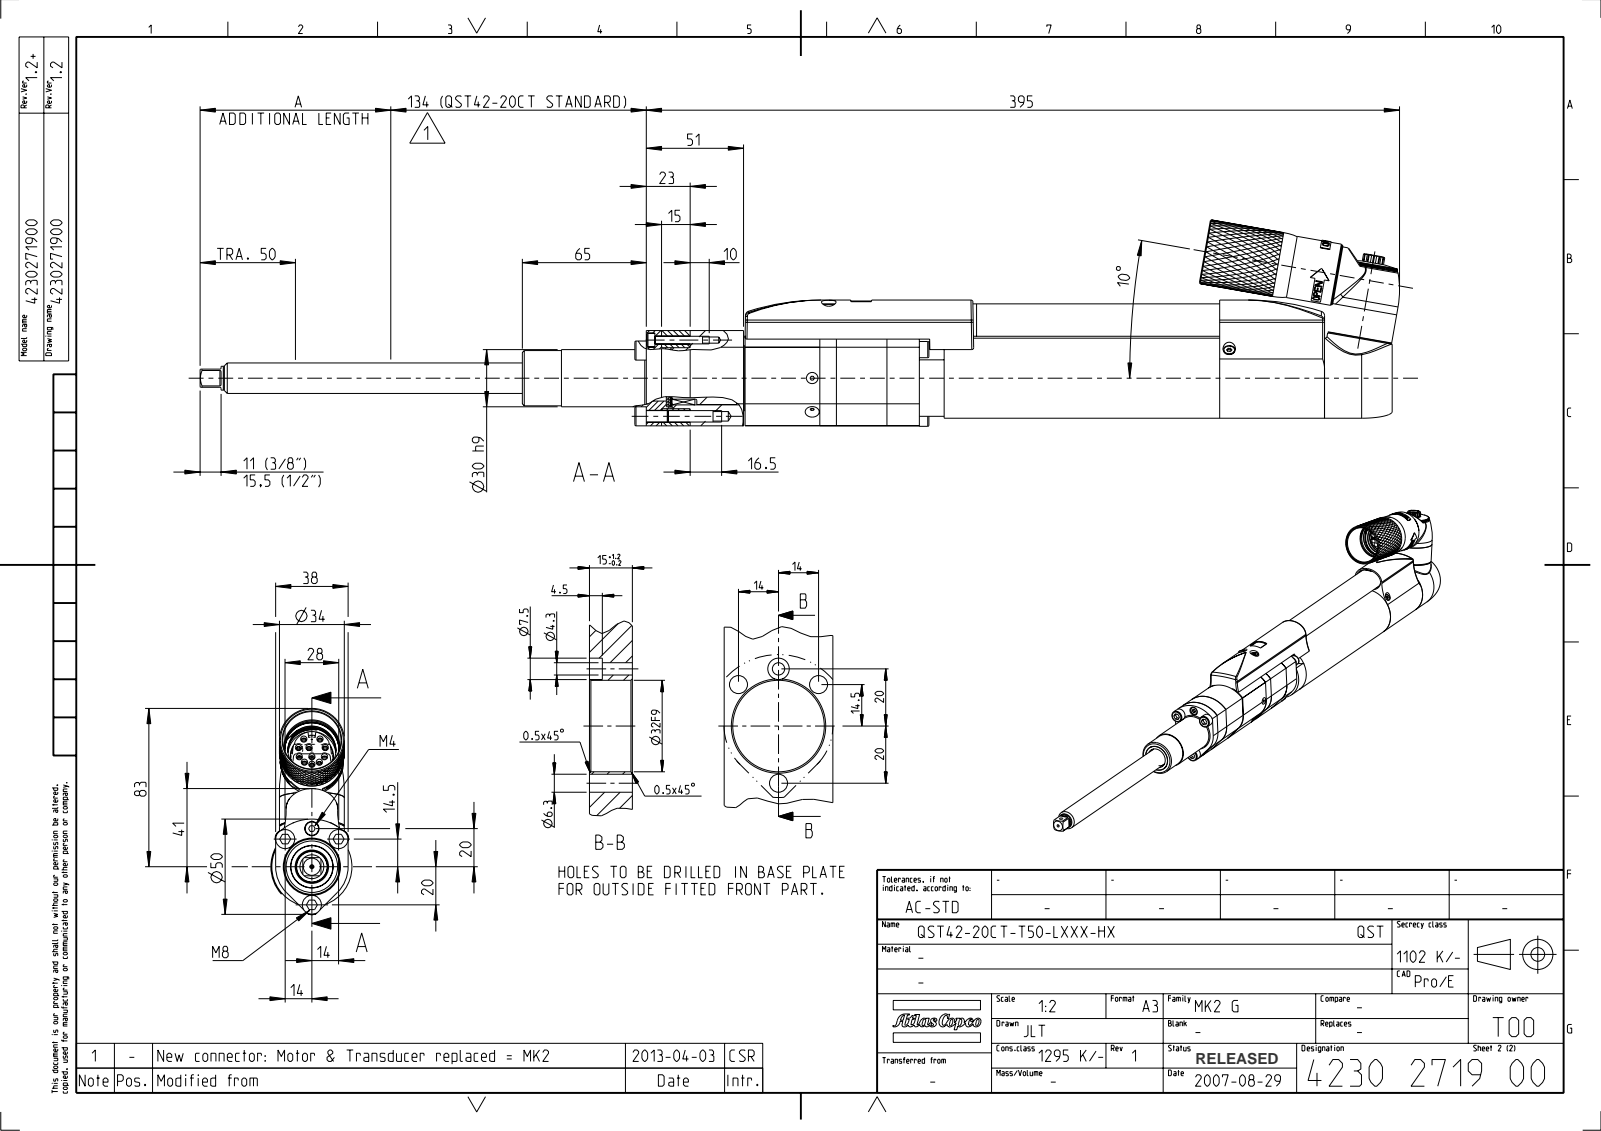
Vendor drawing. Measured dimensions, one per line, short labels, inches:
name: EXT_COMP_SW0009
written by: CREO PARAMETRIC BY PTC INC, 2022414 (AP242_MANAGED_MODEL_BASED_3D_ENGINEERING_MIM_LF)
unit: in
bodies: 2 solids, 1518 faces (722 planar, 344 cylindrical, 452 other)
size: 26.733 × 4.264 × 1.673
volume: 46.99 in³; area: 204.9 in²
holes: 3× ⌀0.163, 2× ⌀0.097, 2× ⌀0.128, 2× ⌀0.177, 1× ⌀0.039, 1× ⌀0.118, 1× ⌀0.138, 1× ⌀0.276, 1× ⌀0.295, 1× ⌀1.205, 1× ⌀1.378
bosses: 4× ⌀1.339, 4× ⌀0.236, 4× ⌀0.118, 3× ⌀0.394, 3× ⌀0.335, 3× ⌀0.276, 2× ⌀1.181, 2× ⌀0.22
rounds: 16× R0.02, 12× R0.011, 12× R0.02, 7× R0.039, 6× R0.008, 4× R0.024, 4× R1.575, 3× R0.256
face distances: 1.496, 0.276, 11.817, 0.354, 8.709, 13.392, 1.575, 9.25, 2.567, 4.142
hole spacings: 0.348, 0.363, 0.472, 0.537, 0.622, 0.835, 1.535, 2.264
